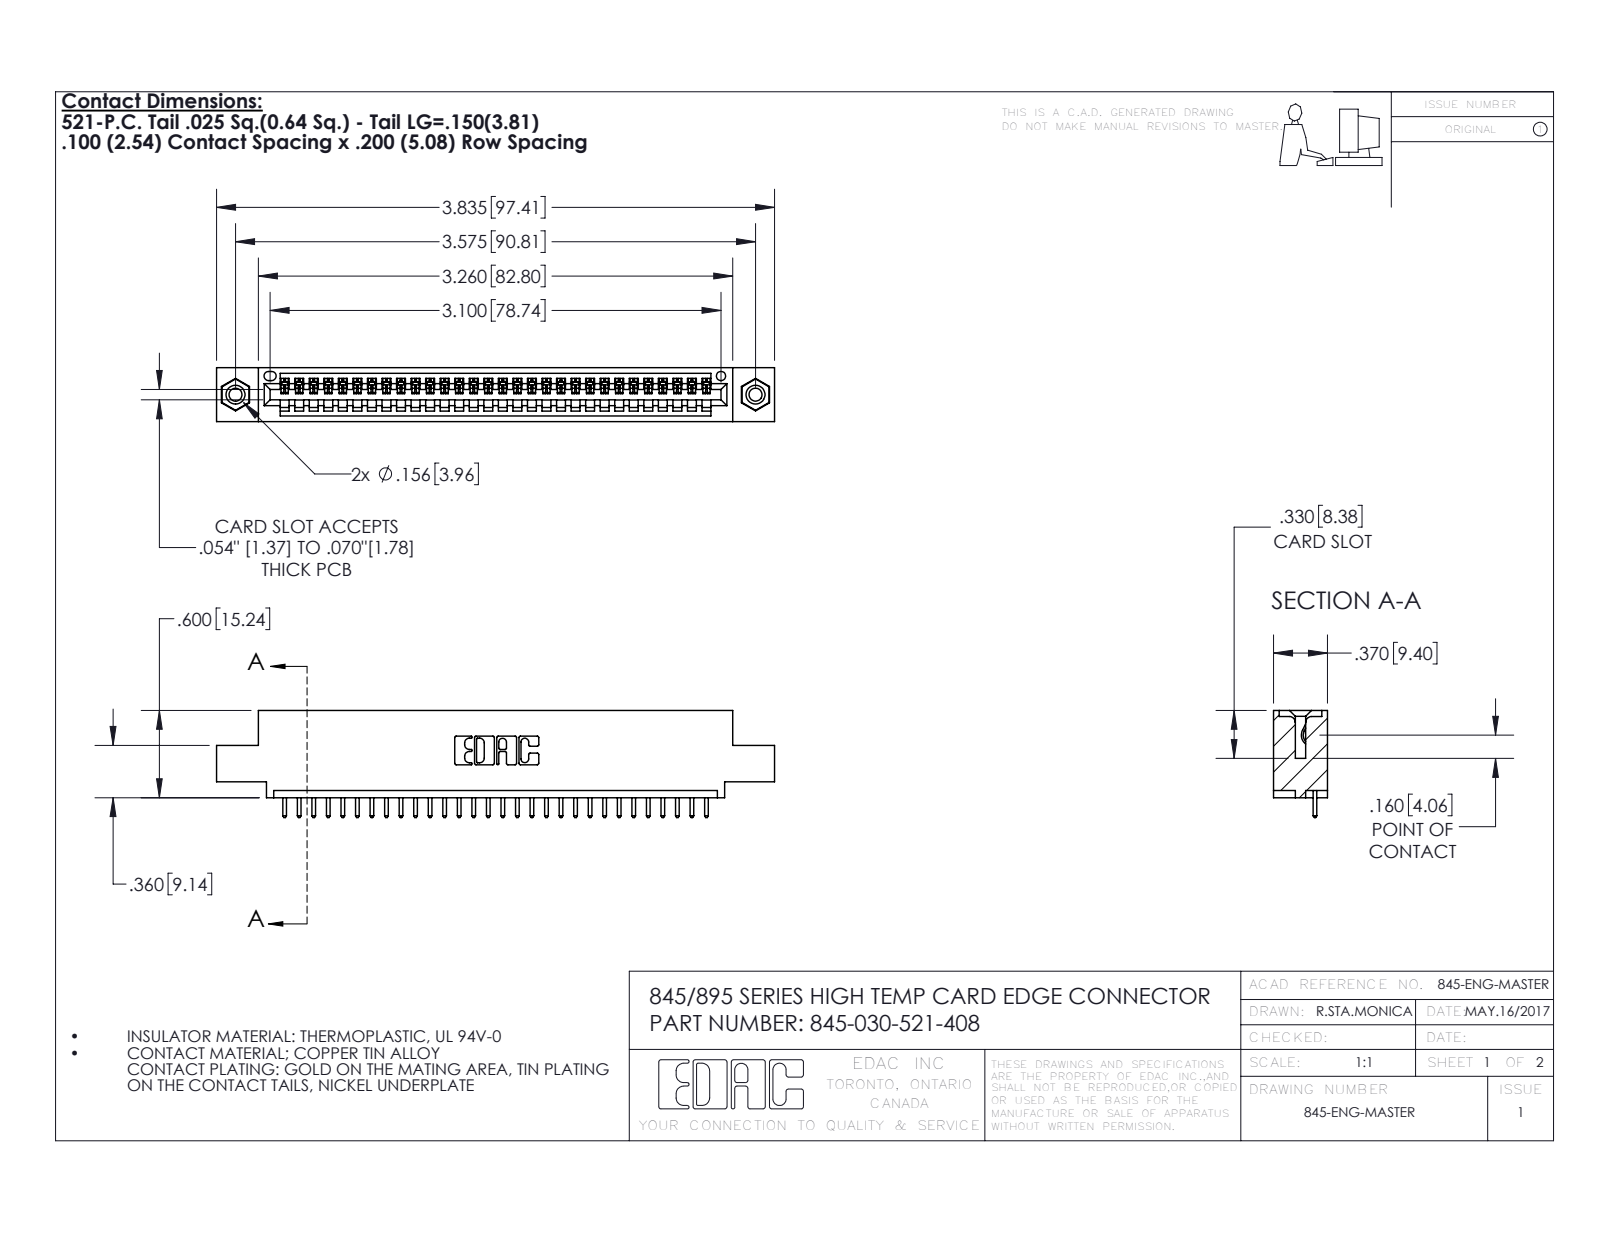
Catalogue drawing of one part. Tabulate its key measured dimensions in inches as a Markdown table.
| quantity | value |
| --- | --- |
| part name | 345-030-521-408; 345 Part_0.110 Offset - 0.156 Dia-TI; 345-250-001_345-250-003-102; 345-292-001_345-293-121 |
| STEP written by | SolidWorks 2016 (CONFIG_CONTROL_DESIGN) |
| units | inches |
| bodies | 33 solids, 1930 faces (1316 planar, 598 cylindrical, 16 other) |
| overall size | 3.835 × 0.737 × 0.37 |
| volume | 0.549 in³ |
| surface area | 17.9 in² |
| round holes (diameter × count) | 0.089 × 2, 0.125 × 2, 0.156 × 2, 0.064 × 1 |
| round bosses / shafts (diameter × count) | 0.155 × 2 |
| partial cylindrical surfaces (radius × count) | 0.006 × 60, 0.01 × 60, 0.01 × 22, 0.007 × 6, 0.031 × 6, 0.026 × 3, 0.031 × 2, 0.04 × 2 |
| main face-to-face distances | 0.072, 0.298, 0.37, 0.2, 0.098, 0.272, 0.025, 0.225, 0.149, 0.072 |
| hole center spacings | 0.27, 3.34, 3.575 |
